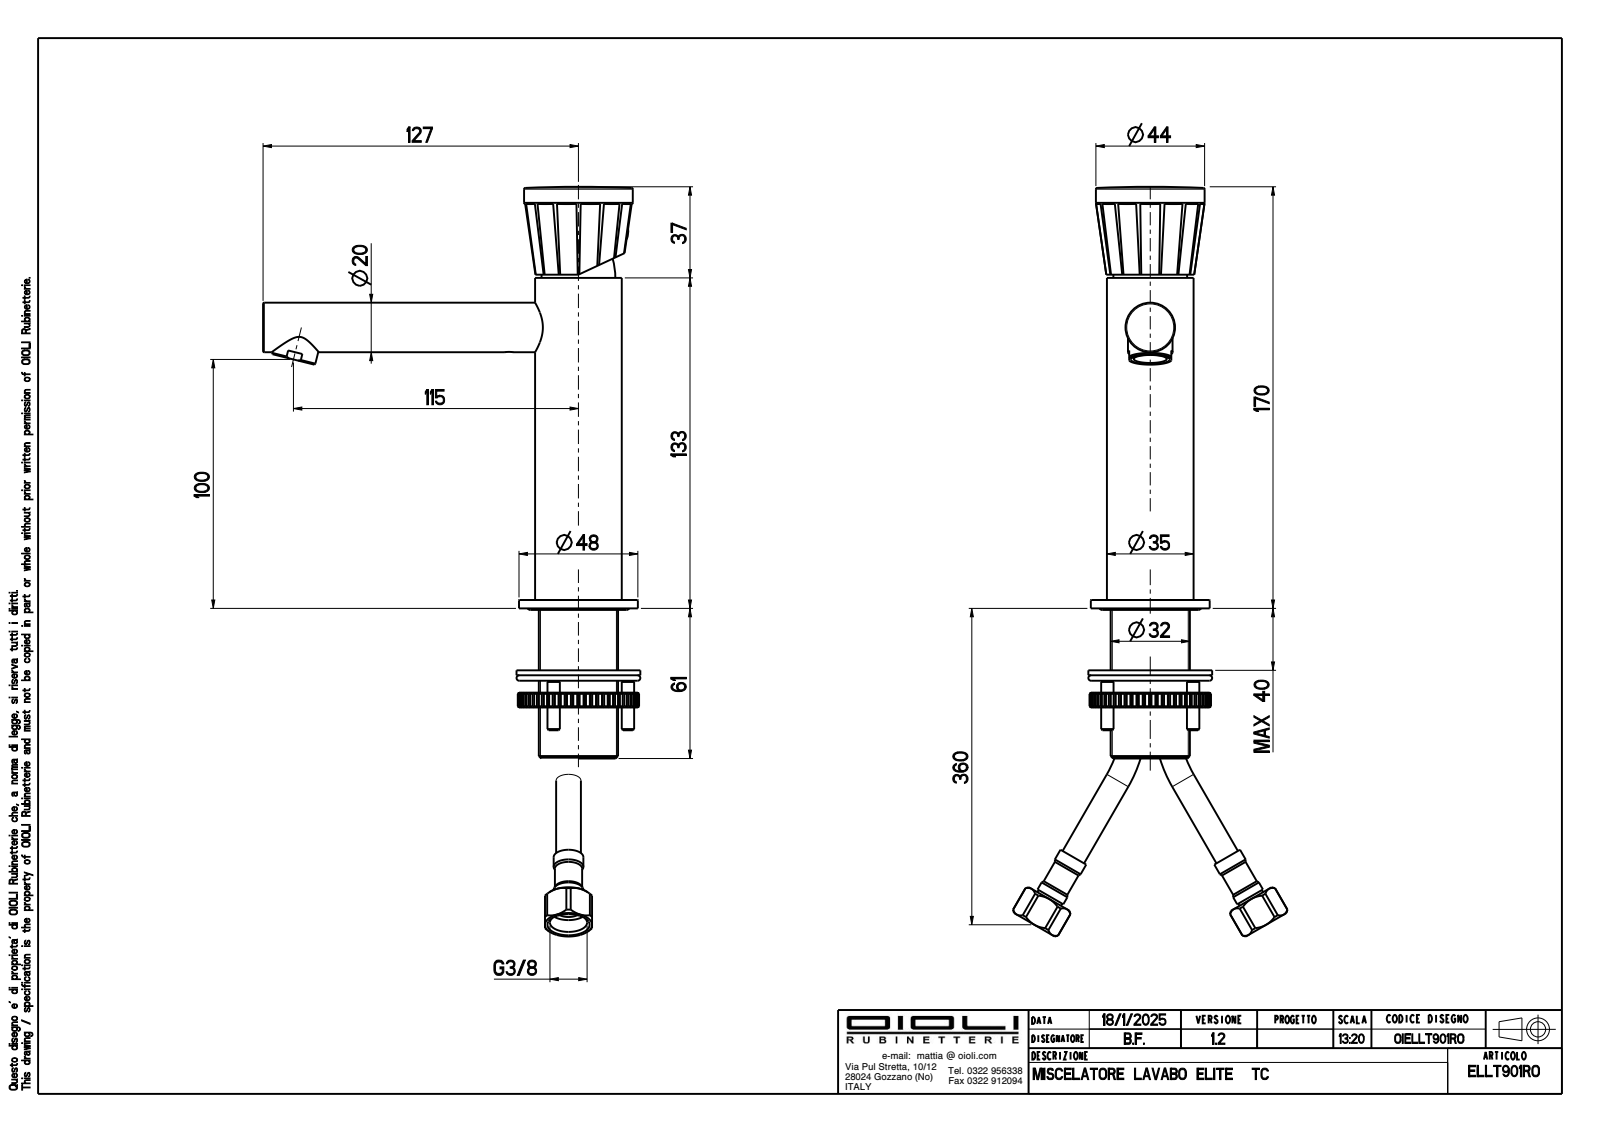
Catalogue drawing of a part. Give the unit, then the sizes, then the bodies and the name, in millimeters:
Units: millimetres
Overall size (bounding box): 170.18 × 151.36 × 48
Round holes (diameter × count): ⌀3.2 ×2, ⌀5 ×2, ⌀7 ×2, ⌀9 ×2, ⌀11 ×2, ⌀15.5 ×2, ⌀3.3 ×1, ⌀4 ×1, ⌀4.2 ×1, ⌀5.3 ×1, ⌀6 ×1, ⌀6.5 ×1
Round bosses / shafts (diameter × count): ⌀16.5 ×2, ⌀8 ×2, ⌀48 ×1, ⌀43.9 ×1, ⌀35.6 ×1, ⌀35 ×1, ⌀32 ×1, ⌀27 ×1
Partial cylindrical surfaces — rounded edges, fillets, slot ends (radius × count): R0.1 ×10, R8.5 ×1
Main face-to-face distances: 163.8, 28, 3.4, 167.2, 83.4, 80, 83.8, 133.4, 130, 50
Hole centre spacings: 1.9, 6.72, 7.63, 8.14, 8.94, 9.33, 11.27, 15.46
Volume: 91 166 mm³ · Surface area: 61 263 mm²
Bodies: 9 solids, 371 faces (111 planar, 147 cylindrical, 113 other)
Part name (STEP PRODUCT): OIBR00322; OIBR00605; OIBR00318; OIVT00002 (+6 more)
STEP written by: CREO PARAMETRIC BY PTC INC, 2024493 (CONFIG_CONTROL_DESIGN)
